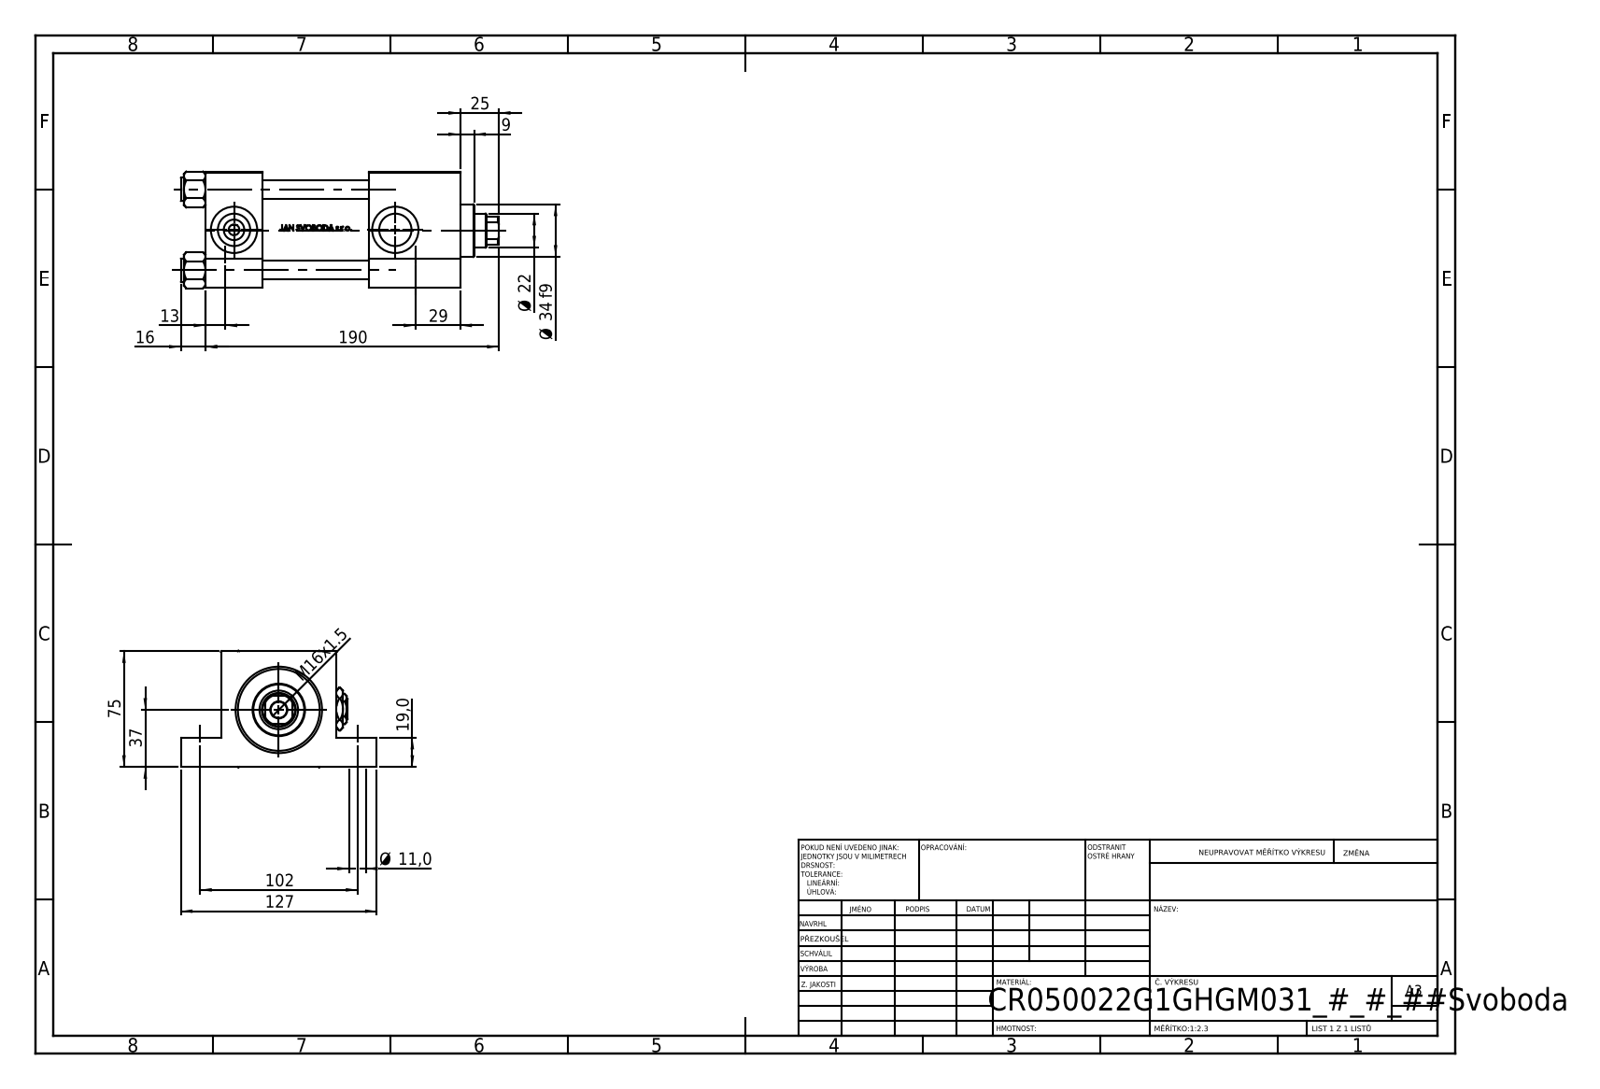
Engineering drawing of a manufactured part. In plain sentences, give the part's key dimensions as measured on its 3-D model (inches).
The part is named "V215CR_G_Body; V215CR_G_TYCINKA; NUT_M5_G; V215_VC_A (+2 more)". Its 3-D file was written by "SolidWorks 2019 (CONFIG_CONTROL_DESIGN)". It is 12 solids with 1134 faces: 454 planar, 128 cylindrical and 552 other. Overall it measures 8.11 by 5 by 2.974 inches. Its volume is 46.81 cubic inches and its surface area 259.4 square inches. Round holes: 4 of diameter 0.433, 4 of diameter 0.472, 2 of diameter 0.276, 2 of diameter 0.825, 2 of diameter 1.181, 1 of diameter 0.413, 1 of diameter 0.866, 1 of diameter 0.984, 1 of diameter 1.614, 1 of diameter 1.969, 1 of diameter 2.087. Round bosses or shafts: 4 of diameter 0.591, 1 of diameter 2.205, 1 of diameter 1.339. Partial cylindrical surfaces (rounded edges, fillets, slot ends): 1 of radius 0.413. The main face-to-face distances are 2.953, 1.457, 6.496, 5.039, 0.748, 2.205, 4.173, 2.717, 2.323, 1.024. The hole center spacings are 2.059, 1.442, 1.47, 2.912, 4.016, 4.843, 6.291, 4.114.
